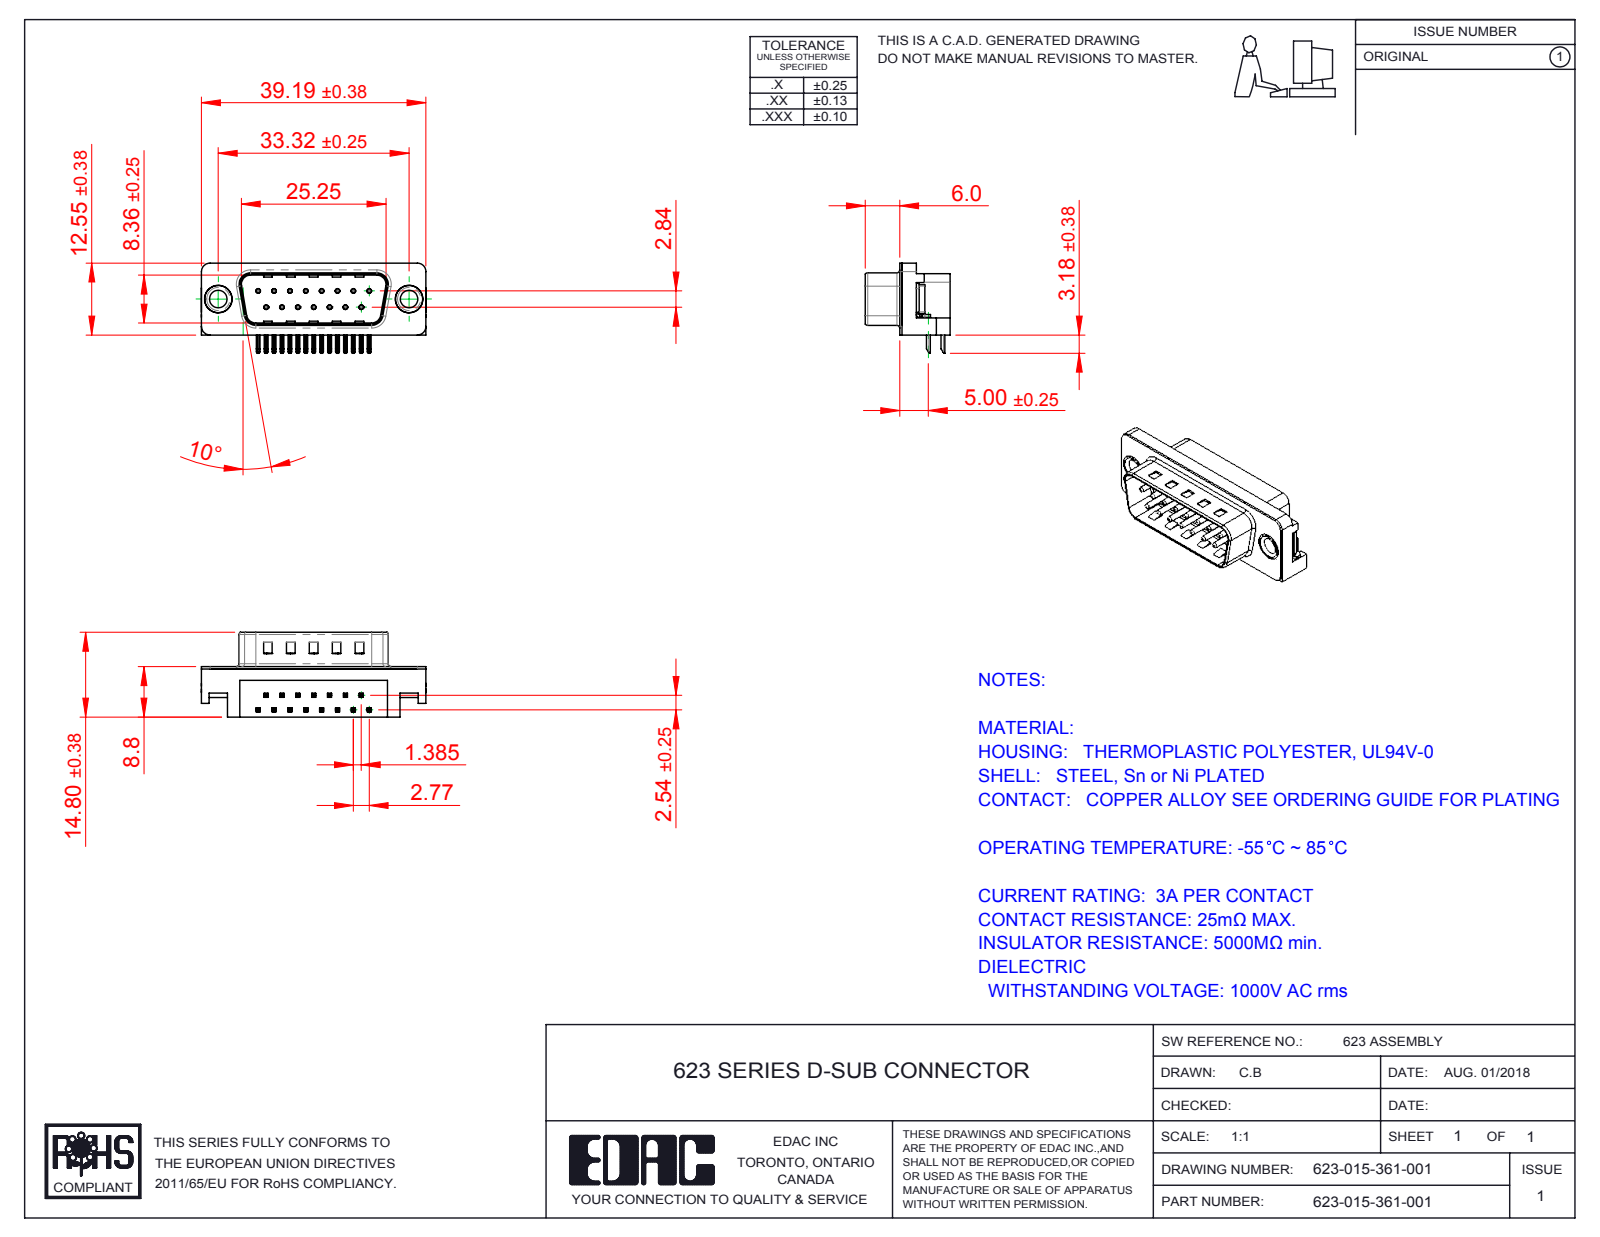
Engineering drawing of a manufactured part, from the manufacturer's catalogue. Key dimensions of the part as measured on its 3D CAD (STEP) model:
Part name (STEP PRODUCT): 623 Contact Bottom; 623 Housing_15 Socket; 623 Shell_15 Socket; 623 Thru Hole Rivet (+3 more)
STEP written by: SolidWorks 2016 (CONFIG_CONTROL_DESIGN)
Units: millimetres
Bodies: 21 solids, 1427 faces (893 planar, 417 cylindrical, 117 other)
Overall size (bounding box): 39.22 × 15.73 × 14.8
Volume: 3 306 mm³ · Surface area: 4 861 mm²
Round holes (diameter × count): ⌀0.35 ×15, ⌀0.8 ×15, ⌀3.05 ×2, ⌀4 ×2, ⌀4.8 ×2, ⌀5 ×2
Round bosses / shafts (diameter × count): ⌀0.75 ×15, ⌀4.9 ×2, ⌀4.75 ×2, ⌀3.85 ×2
Partial cylindrical surfaces — rounded edges, fillets, slot ends (radius × count): R0.25 ×68, R0.12 ×30, R1 ×16, R0.5 ×9, R1.5 ×6, R0.9 ×4, R1.6 ×4, R2 ×4
Main face-to-face distances: 0.4, 8.4, 2.1, 1.7, 8.8, 10.46, 10.86, 8.76, 5.9, 2.9
Hole centre spacings: 3.16, 2.77, 5.54, 8.31, 11.08, 5.03, 5.04, 7.48
